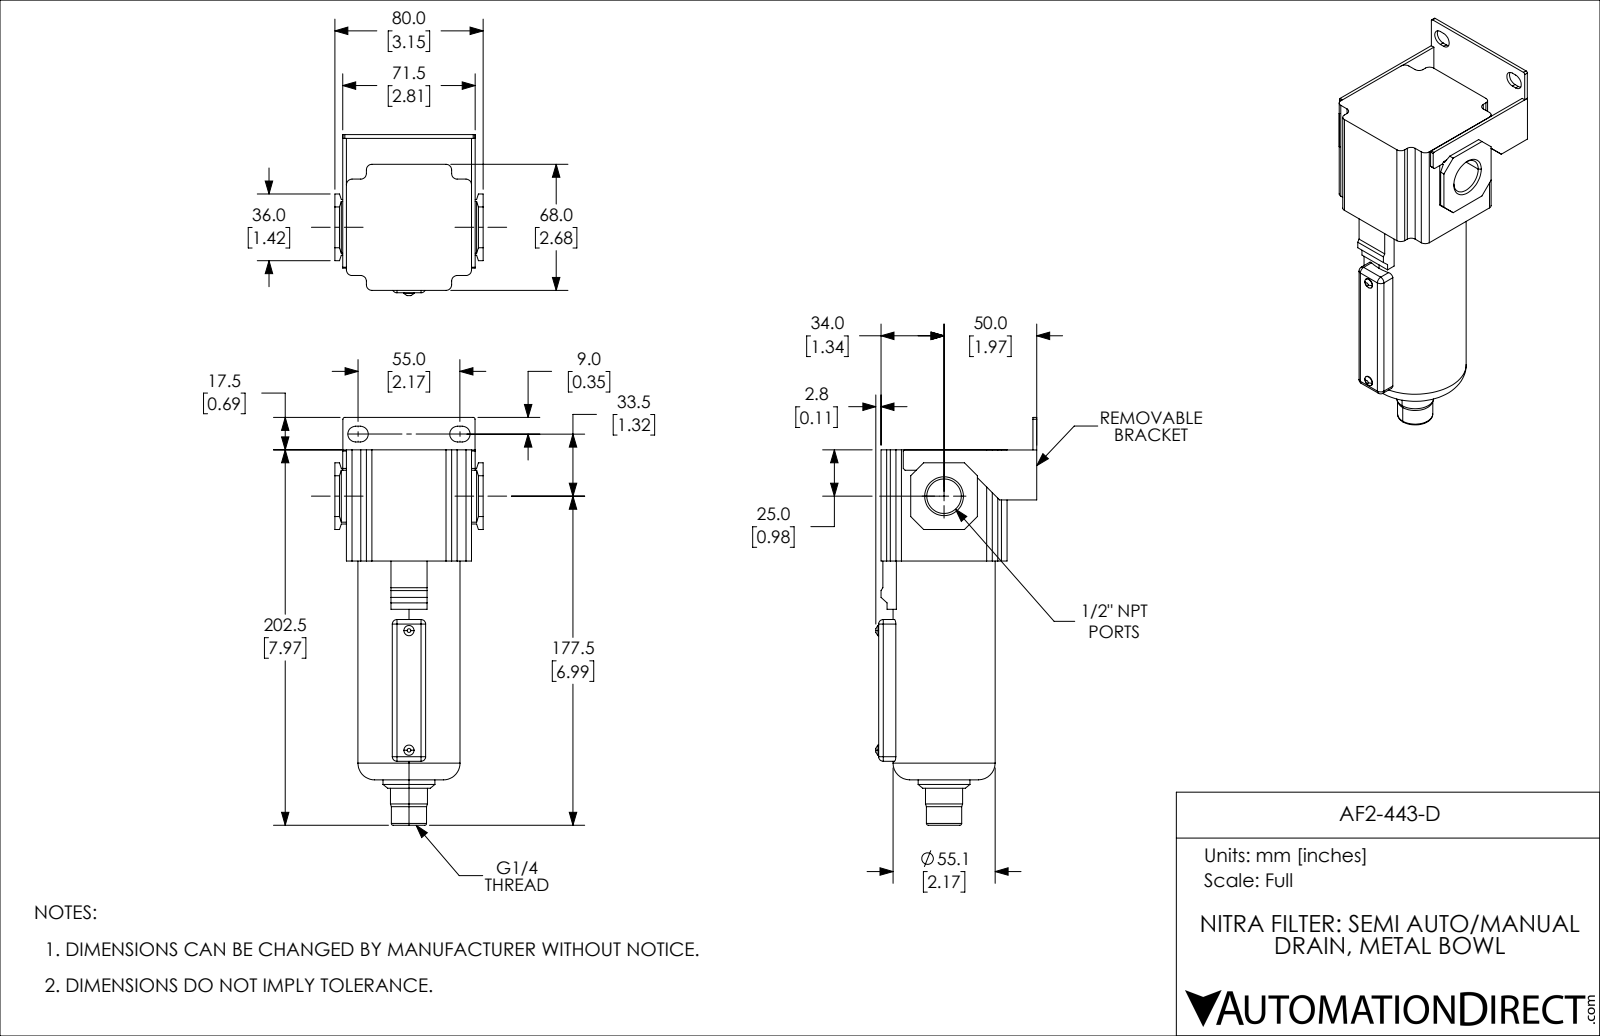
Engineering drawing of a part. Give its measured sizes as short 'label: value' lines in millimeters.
name: AF2-443-D
written by: SolidWorks 2019 (CONFIG_CONTROL_DESIGN)
unit: mm
bodies: 1 solid, 161 faces (95 planar, 44 cylindrical, 22 other)
size: 220 × 86.8 × 80
volume: 567 219 mm³; area: 61 405 mm²
holes: 1× ⌀8.57, 1× ⌀18.63
bosses: 2× ⌀5.5, 1× ⌀55.1, 1× ⌀28, 1× ⌀20, 1× ⌀19
rounds: 12× R3, 8× R2.5, 4× R4.25, 2× R1
face distances: 2, 14, 60, 16, 82, 68, 84, 69.5, 67.5, 4.25
